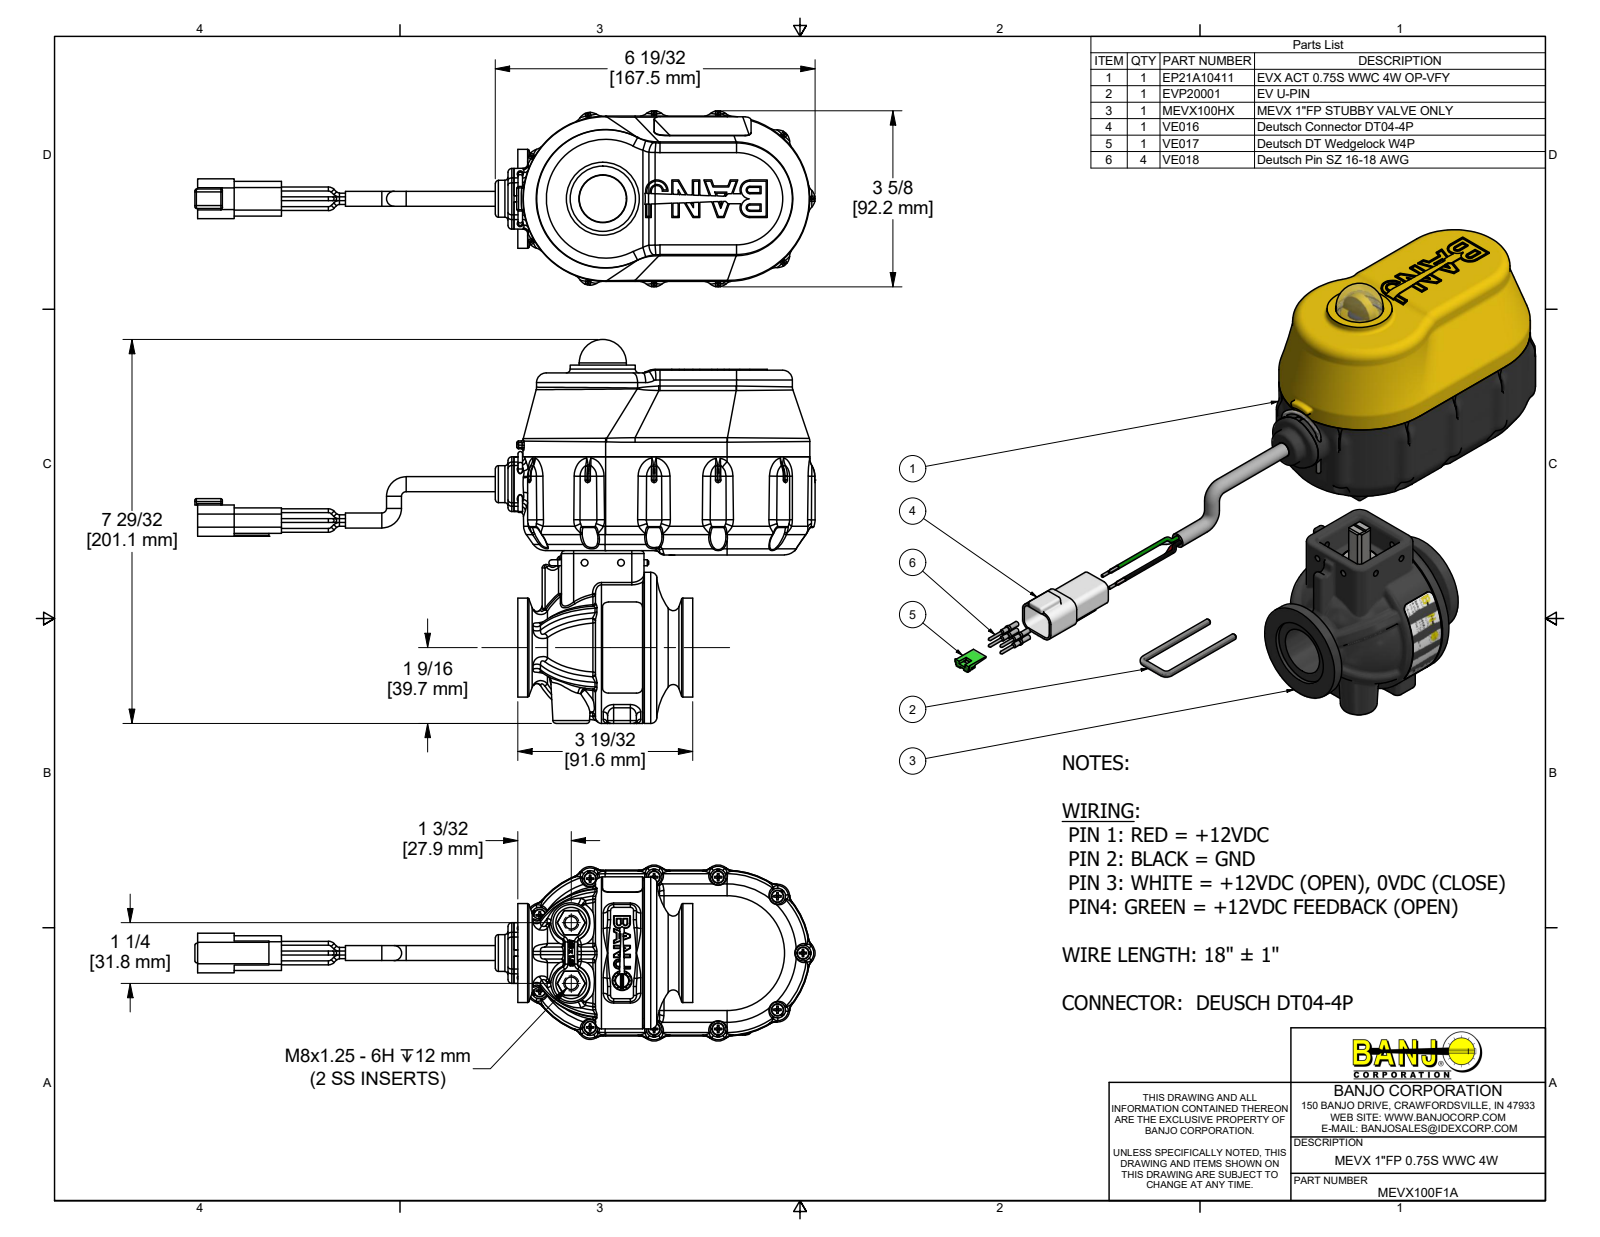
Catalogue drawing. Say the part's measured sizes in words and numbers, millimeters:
The part is named "MEVX100F1A; EP21A10411; B61905PPHS; B632038PM (+8 more)". Its 3-D file was written by "Autodesk Inventor 2019 (AUTOMOTIVE_DESIGN)". It is 90 solids with 11137 faces: 3076 planar, 3165 cylindrical and 4896 other. Overall it measures 324.9 by 201.1 by 92.2 millimeters. Its volume is 769 900 cubic millimeters and its surface area 349 300 square millimeters. Round holes: 11 of diameter 2.4, 11 of diameter 3.8, 8 of diameter 3.8, 7 of diameter 2, 5 of diameter 3.4, 4 of diameter 0.8, 4 of diameter 1.5, 4 of diameter 2.7, 4 of diameter 3.2, 4 of diameter 3.5, 4 of diameter 3.8, 4 of diameter 4.3. Round bosses or shafts: 20 of diameter 2, 17 of diameter 6.4, 11 of diameter 3.6, 11 of diameter 2.7, 11 of diameter 2.2, 8 of diameter 1.5, 4 of diameter 6.9, 4 of diameter 5.6. Partial cylindrical surfaces (rounded edges, fillets, slot ends): 180 of radius 0.3, 145 of radius 1, 84 of radius 0.3, 71 of radius 0.5, 54 of radius 0.1, 48 of radius 1.5, 38 of radius 0.8, 34 of radius 3.2. The main face-to-face distances are 2.5, 65.2, 5.4, 1.5, 3.8, 42.8, 46.6, 48.2, 62.6, 19.8. The hole center spacings are 45.5, 32.6, 67.5, 38.4, 42.2, 68.3, 72.4, 96.2.
